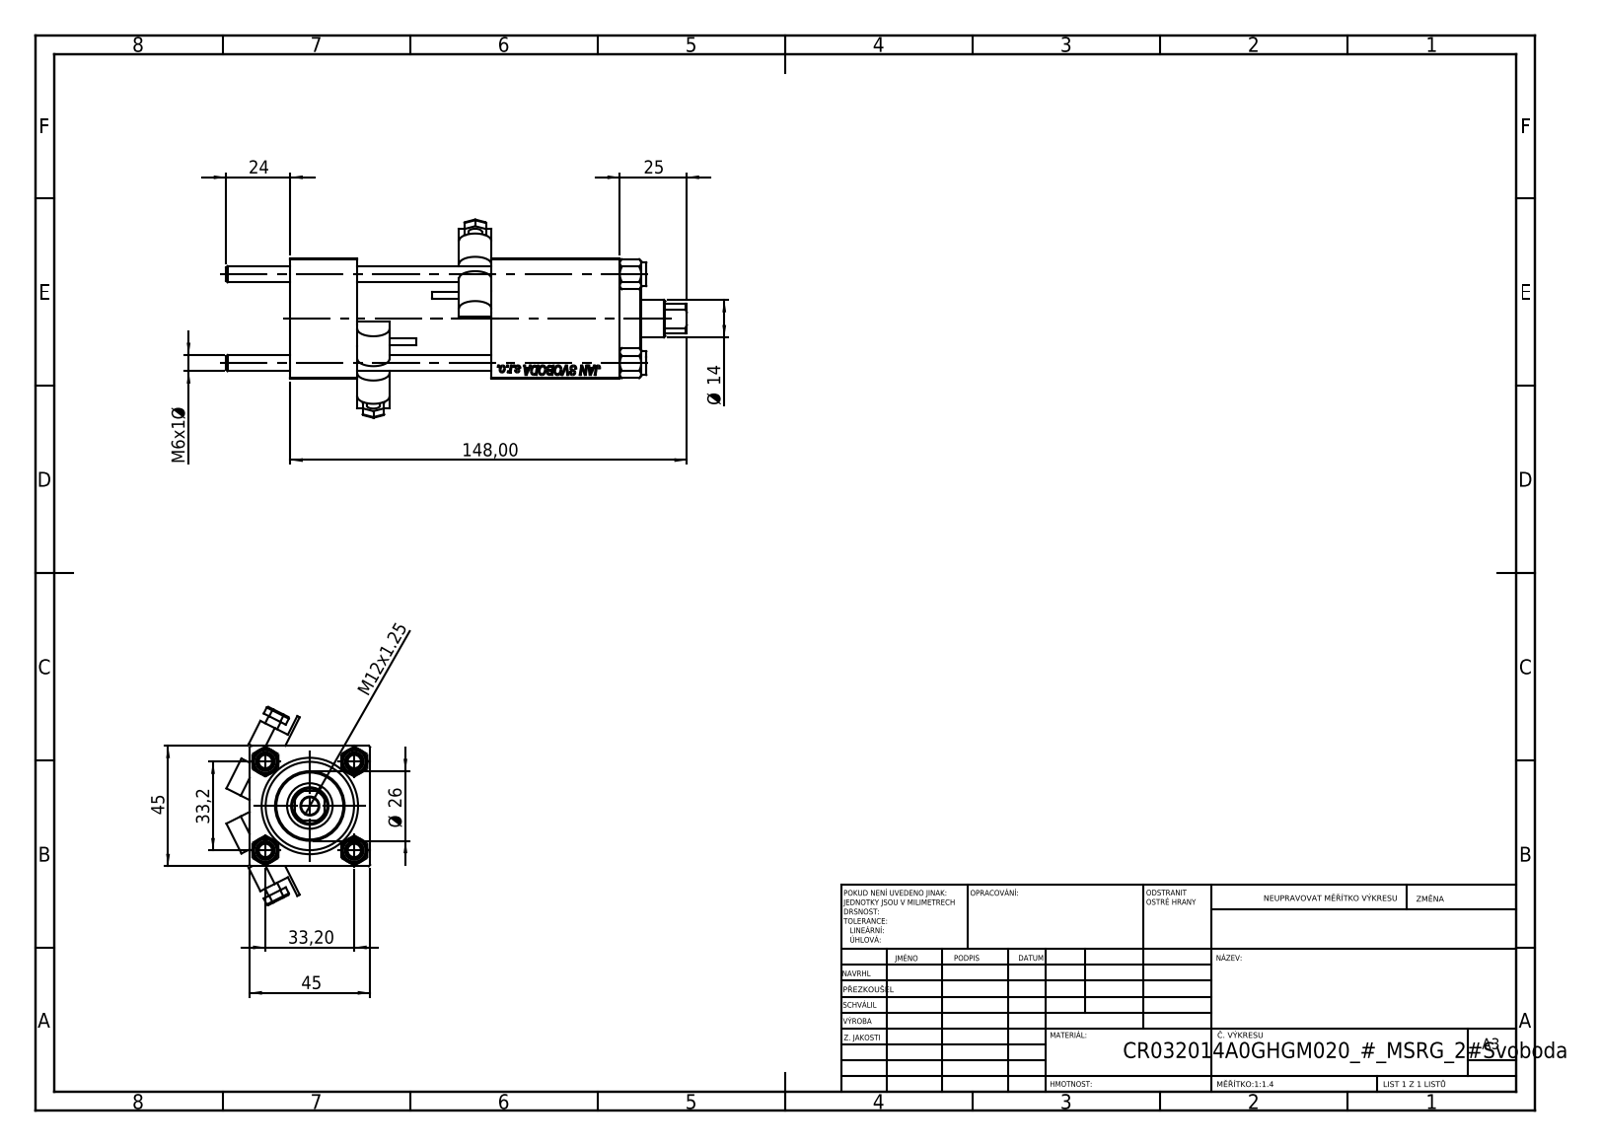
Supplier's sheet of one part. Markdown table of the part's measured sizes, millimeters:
| quantity | value |
| --- | --- |
| part name | V215CR_BODY_A; NUT_M5; V215_VC_A; MSRF_MSRG1 (+2 more) |
| STEP written by | SolidWorks 2019 (CONFIG_CONTROL_DESIGN) |
| units | millimeters |
| bodies | 13 solids, 1197 faces (555 planar, 106 cylindrical, 536 other) |
| overall size | 172 × 74.05 × 53.66 |
| volume | 205 265 mm³ |
| surface area | 77 021 mm² |
| round holes (diameter × count) | 6 × 4, 7 × 2, 13.16 × 2, 20 × 2, 6.5 × 1, 14 × 1, 17 × 1, 24 × 1, 32 × 1, 33 × 1 |
| round bosses / shafts (diameter × count) | 9 × 4, 5 × 2, 2.5 × 2, 38 × 1, 26 × 1 |
| partial cylindrical surfaces (radius × count) | 0.5 × 12, 6 × 4, 6.5 × 1 |
| main face-to-face distances | 45, 25, 123, 98, 50, 48, 75, 94.3, 69.3, 19.3 |
| hole center spacings | 23.48, 33.2, 46.95, 75.5 |
